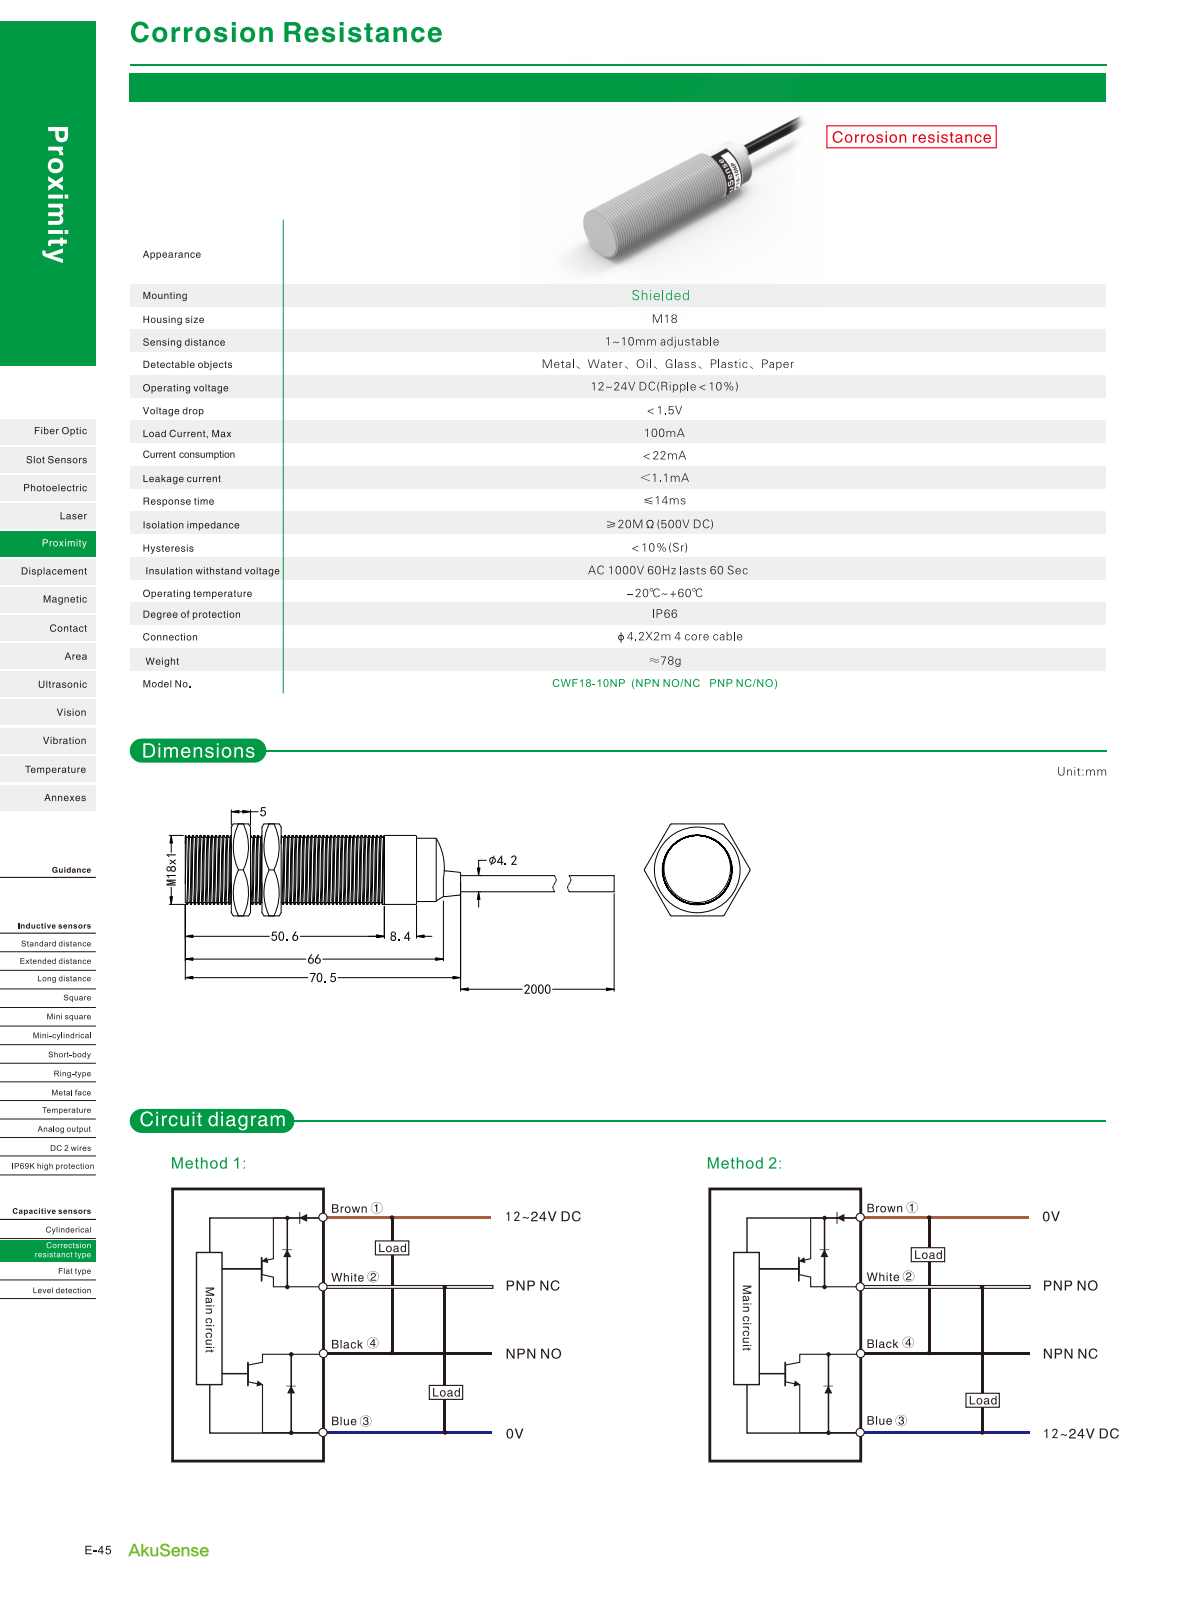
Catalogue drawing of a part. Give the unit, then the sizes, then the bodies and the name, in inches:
Units: inches
Overall size (bounding box): 3.957 × 0.709 × 0.709
Round bosses / shafts (diameter × count): ⌀0.709 ×1, ⌀0.669 ×1, ⌀0.551 ×1, ⌀0.165 ×1
Main face-to-face distances: 2.598, 0.276, 2.323, 0.606, 0.331, 1.992, 1.358, 1.634, 1.965, 3.957
Volume: 0.999 in³ · Surface area: 9.742 in²
Bodies: 1 solid, 139 faces (7 planar, 119 cylindrical, 13 other)
Part name (STEP PRODUCT): CWF18-10NP
STEP written by: SolidWorks 2016 (CONFIG_CONTROL_DESIGN)
